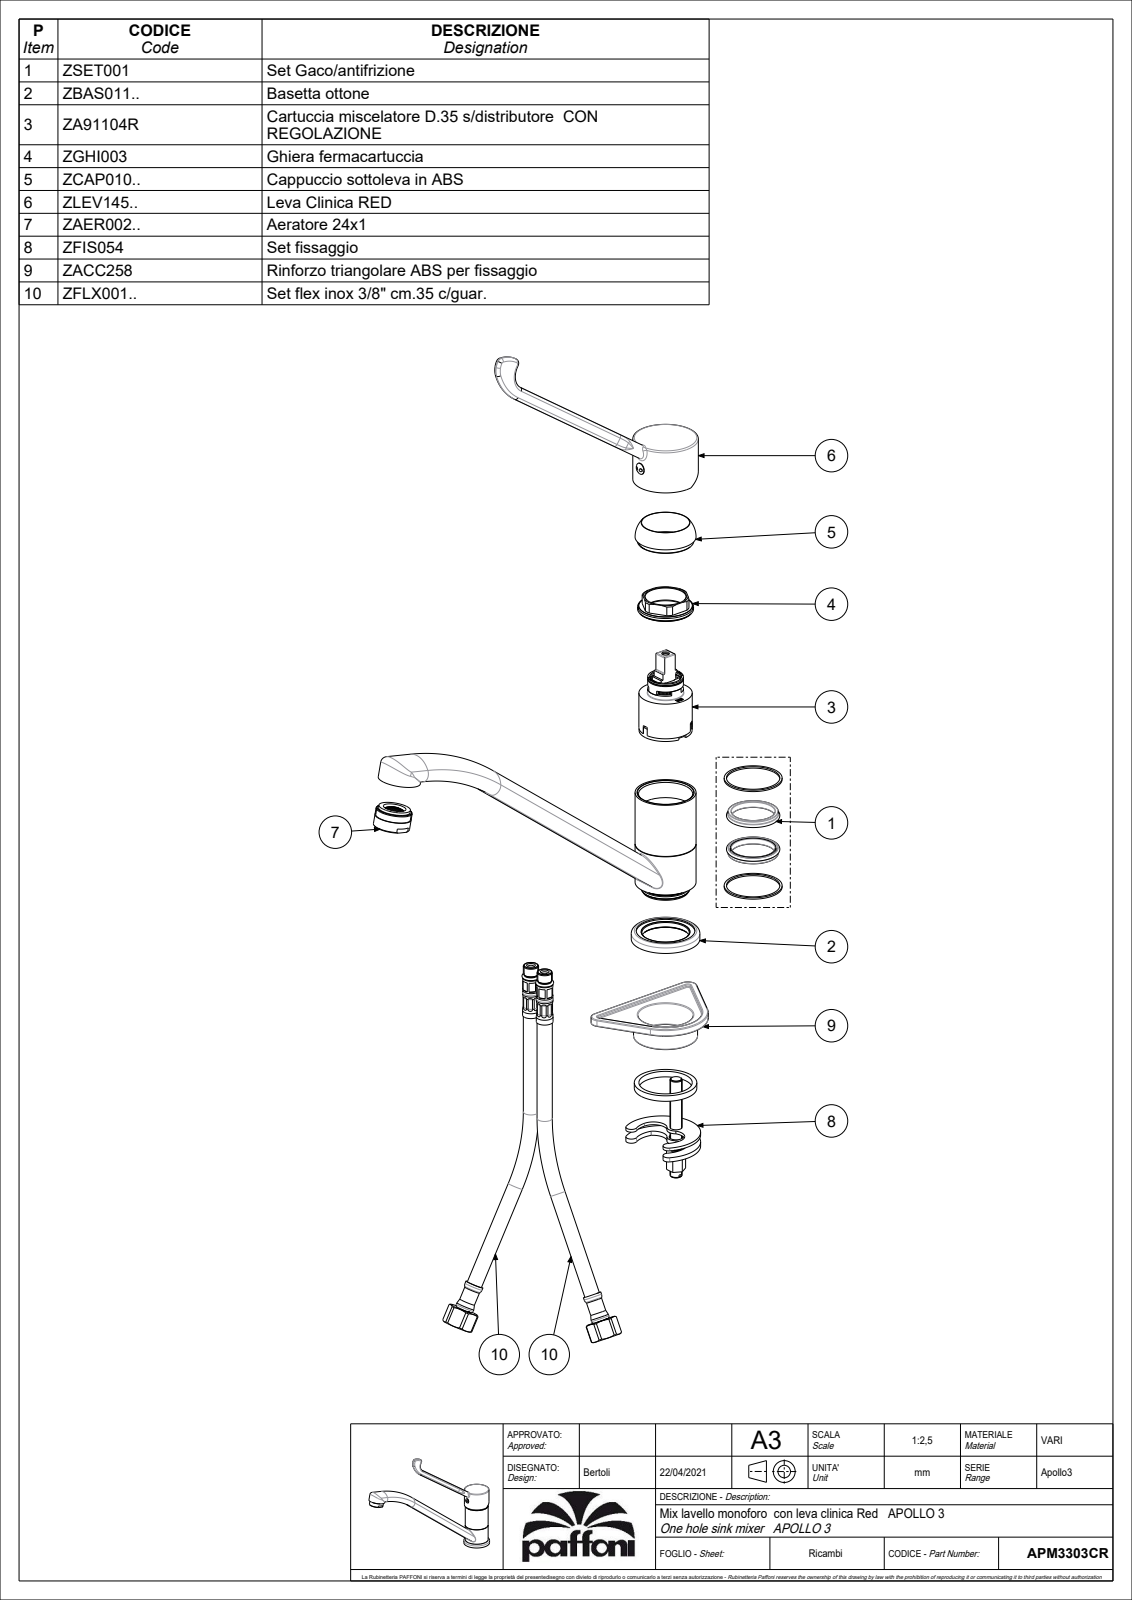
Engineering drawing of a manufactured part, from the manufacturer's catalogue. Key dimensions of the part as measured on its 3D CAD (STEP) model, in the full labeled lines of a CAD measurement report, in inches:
Part name (STEP PRODUCT): APM3303CR
STEP written by: CREO PARAMETRIC BY PTC INC, 2021404 (CONFIG_CONTROL_DESIGN)
Units: inches
Bodies: 3 solids, 2551 faces (1949 planar, 341 cylindrical, 261 other)
Overall size (bounding box): 10.401 × 7.983 × 1.772
Volume: 6.294 in³ · Surface area: 151.2 in²
Round holes (diameter × count): ⌀0.315 ×3, ⌀0.354 ×3, ⌀0.157 ×2, ⌀0.433 ×2, ⌀0.118 ×1, ⌀0.13 ×1, ⌀0.177 ×1, ⌀0.197 ×1, ⌀0.276 ×1, ⌀0.335 ×1, ⌀0.591 ×1, ⌀0.63 ×1
Round bosses / shafts (diameter × count): ⌀1.772 ×1, ⌀1.693 ×1, ⌀1.575 ×1, ⌀1.378 ×1, ⌀1.37 ×1, ⌀1.268 ×1, ⌀1.26 ×1, ⌀1.24 ×1
Partial cylindrical surfaces — rounded edges, fillets, slot ends (radius × count): R0.02 ×66, R0.006 ×11, R0.012 ×4, R0.079 ×4, R0.185 ×4, R0.217 ×4, R0.039 ×2, R0.618 ×2
Main face-to-face distances: 0.031, 0.177, 0.039, 0.02, 3.839, 0.236, 2.445, 0.118, 2.425, 0.079
Hole centre spacings: 0.02, 0.328, 0.339, 0.457, 0.472, 0.551, 0.552, 0.599
